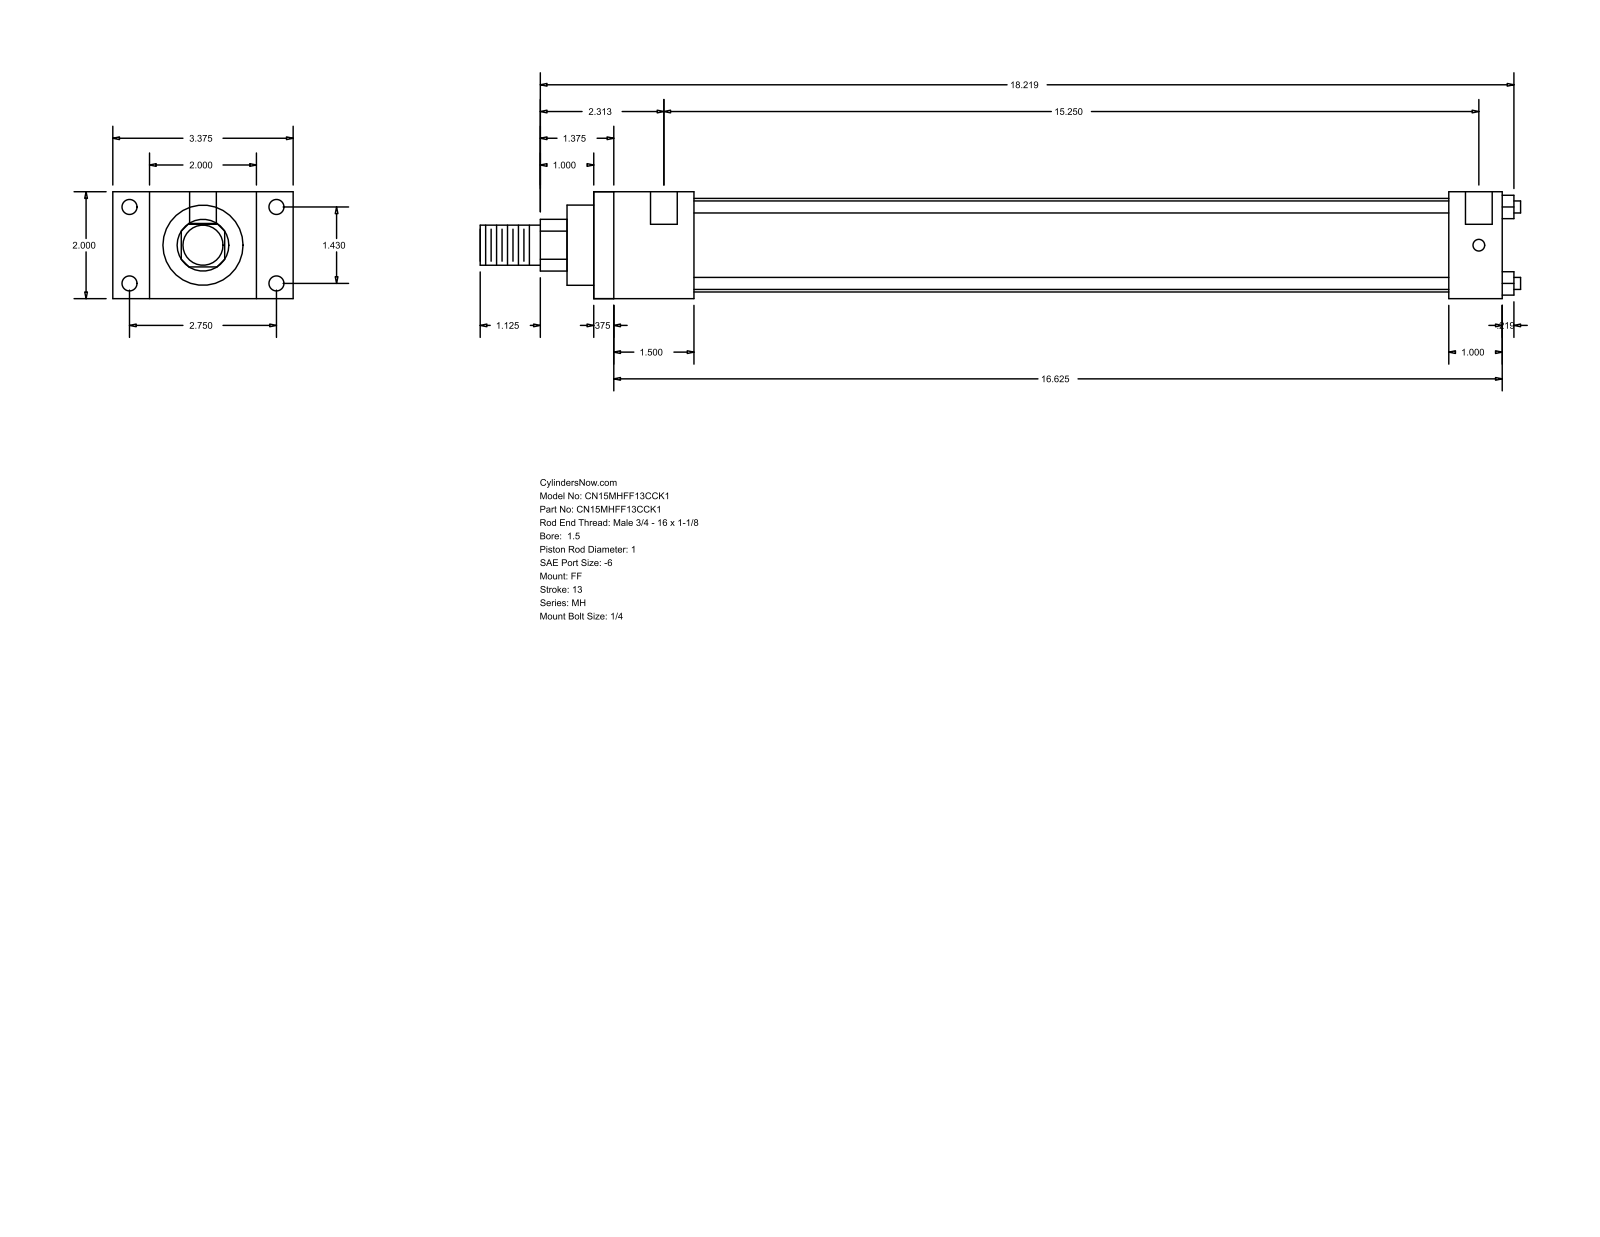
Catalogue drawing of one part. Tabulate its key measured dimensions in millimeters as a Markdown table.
| quantity | value |
| --- | --- |
| part name | MH_FF__0150_1 |
| STEP written by | GSSL Pune (CONFIG_CONTROL_DESIGN) |
| units | millimeters |
| bodies | 0 solids, 92 faces (64 planar, 28 cylindrical, 0 other) |
| overall size | 494.51 × 85.72 × 50.8 |
| round holes (diameter × count) | 5.56 × 4, 7.14 × 4, 12.7 × 2 |
| round bosses / shafts (diameter × count) | 5.71 × 4, 44.45 × 1, 38.1 × 1, 25.4 × 1, 19.05 × 1 |
| partial cylindrical surfaces (radius × count) | 12.29 × 1 |
| main face-to-face distances | 50.8, 431.8, 9.52, 422.28, 25.4, 17.46, 68.26, 47.63, 38.11, 384.17 |
| hole center spacings | 36.32, 69.84, 78.72, 390.53, 3.18, 387.35 |
